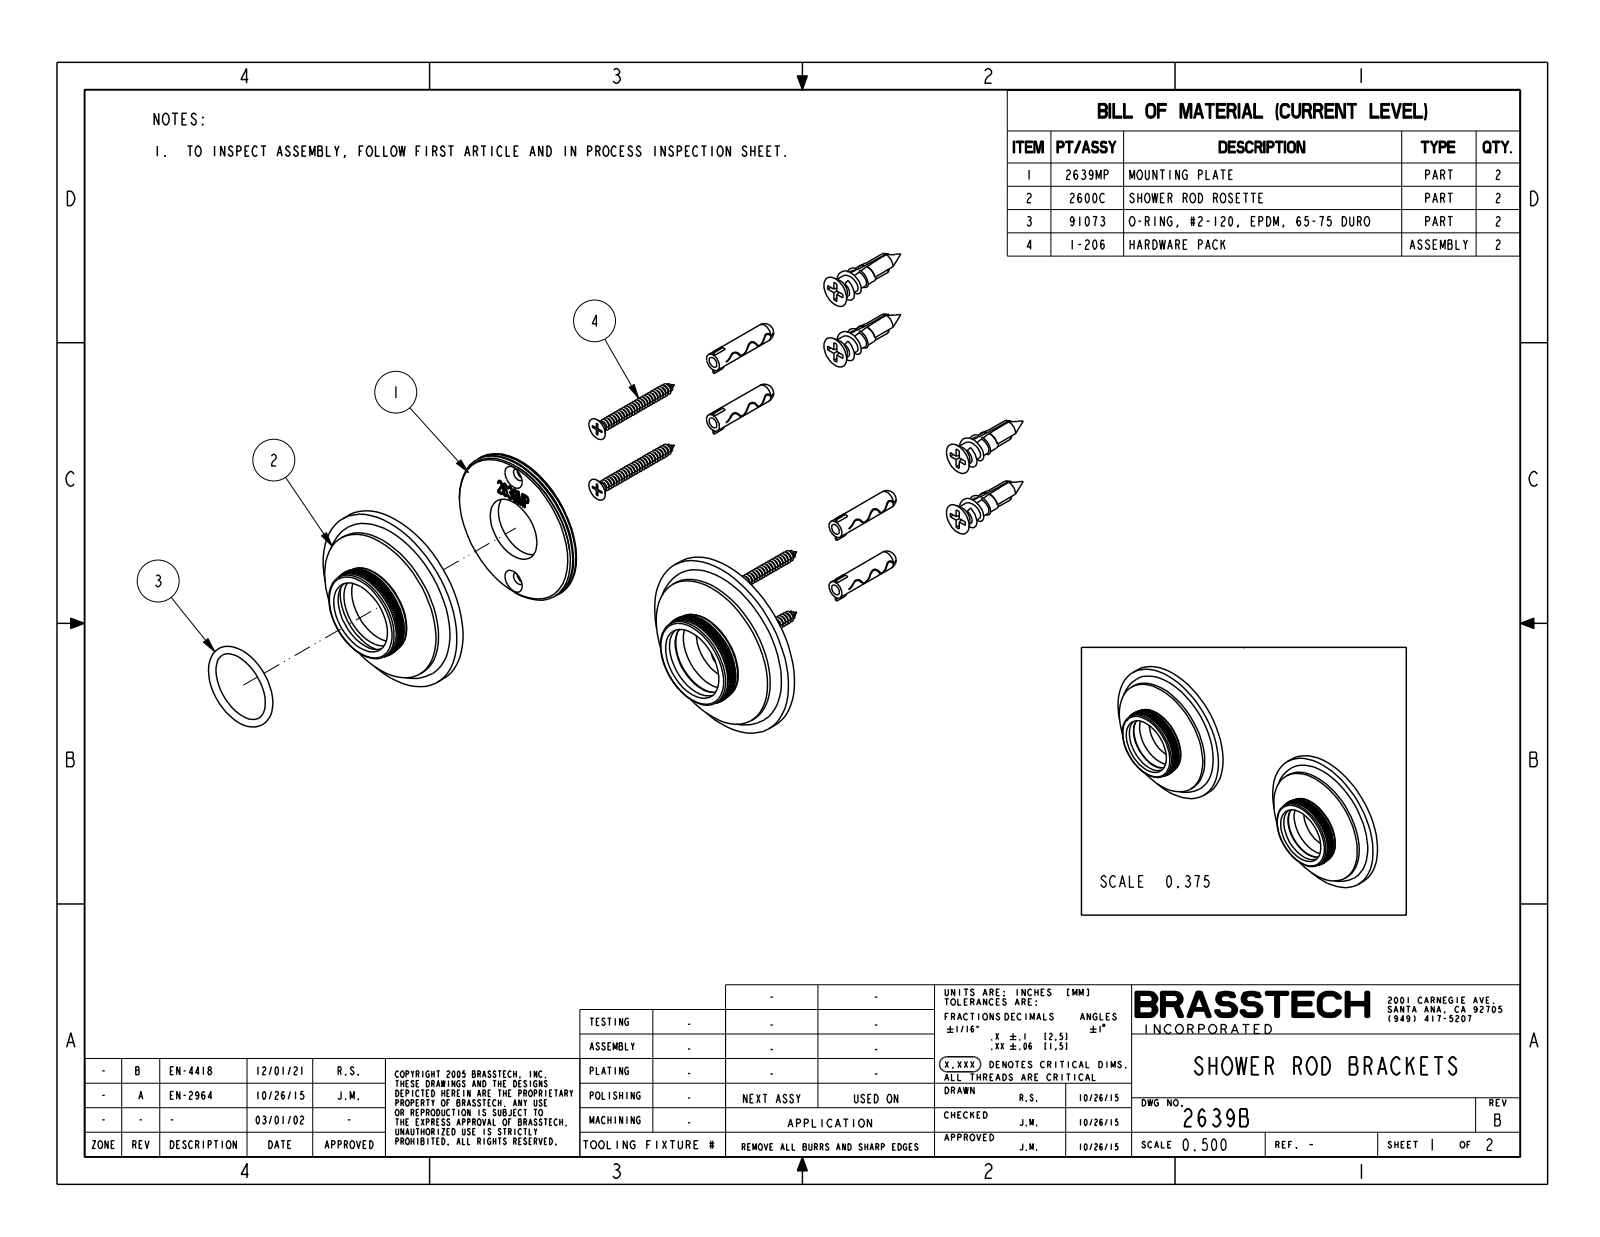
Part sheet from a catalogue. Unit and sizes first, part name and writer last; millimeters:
Units: millimetres
Overall size (bounding box): 167.6 × 66 × 17.5
Round holes (diameter × count): ⌀4.5 ×4, ⌀23 ×2, ⌀26.4 ×2, ⌀30.3 ×2, ⌀51.3 ×2, ⌀53.4 ×2
Round bosses / shafts (diameter × count): ⌀66 ×2, ⌀54.9 ×2, ⌀32 ×2
Partial cylindrical surfaces — rounded edges, fillets, slot ends (radius × count): R0.1 ×416, R27.5 ×2
Main face-to-face distances: 4, 3, 1, 12.5, 17.5, 14.5, 13.5, 2.4, 12.1, 5.4
Hole centre spacings: 22.2, 104, 101.6, 44.5, 110.9
Volume: 33 890 mm³ · Surface area: 30 280 mm²
Bodies: 2 solids, 1612 faces (1016 planar, 534 cylindrical, 62 other)
Part name (STEP PRODUCT): 2639B
STEP written by: CREO PARAMETRIC BY PTC INC, 2018400 (CONFIG_CONTROL_DESIGN)
